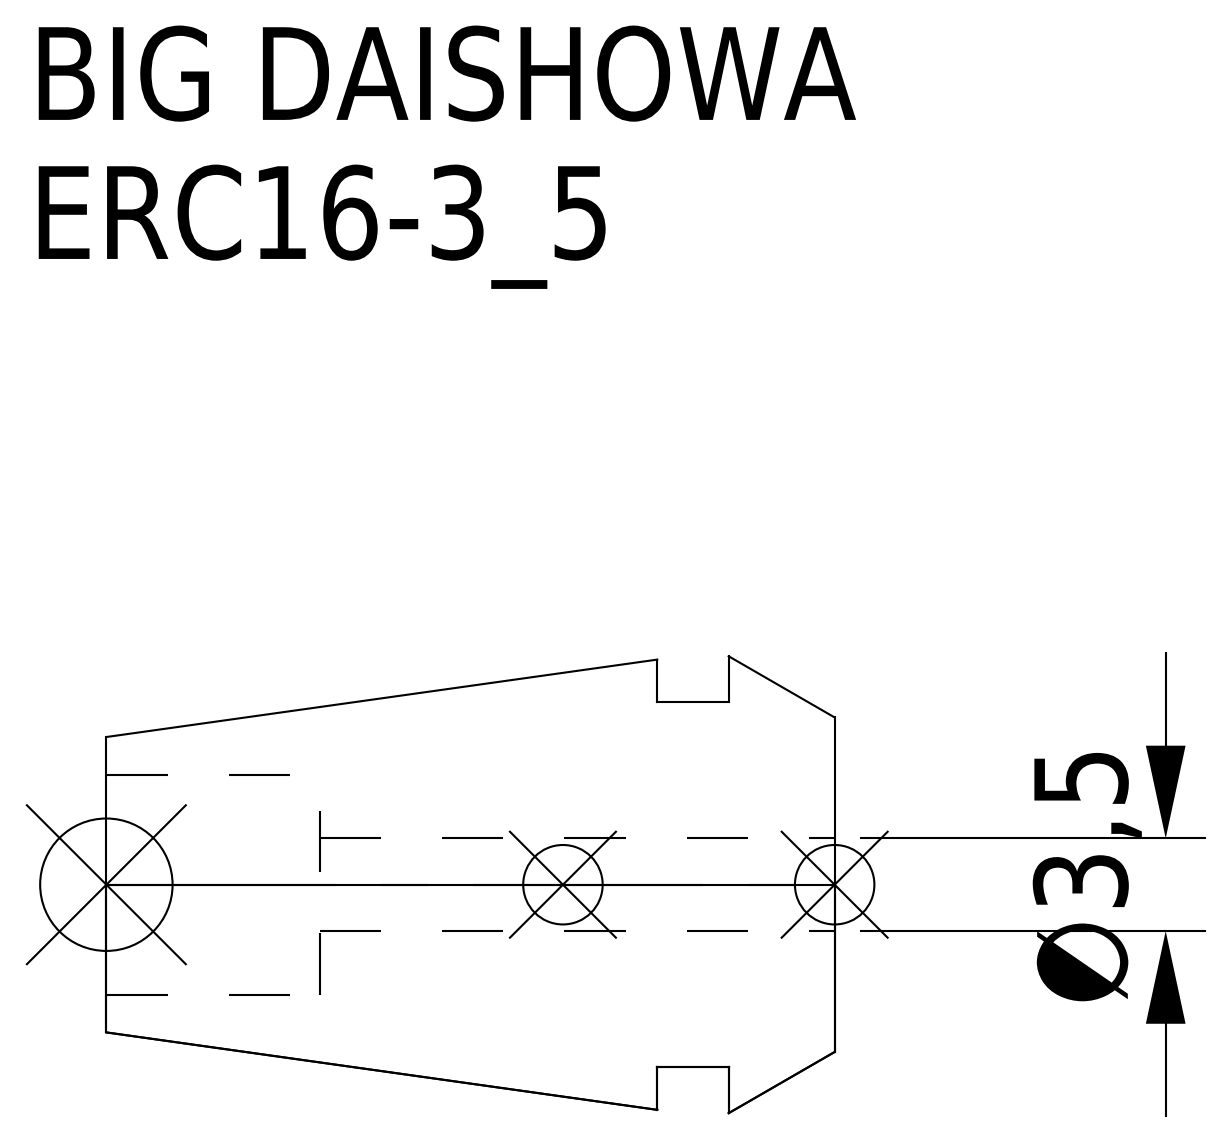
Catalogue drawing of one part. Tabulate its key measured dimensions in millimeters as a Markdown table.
| quantity | value |
| --- | --- |
| part name | ERC16-3_5 |
| STEP written by | CREO PARAMETRIC BY PTC INC, 2016380 (AUTOMOTIVE_DESIGN) |
| units | millimeters |
| bodies | 1 solid, 15 faces (5 planar, 6 cylindrical, 4 other) |
| overall size | 27.5 × 17.25 × 17.25 |
| volume | 3 772 mm³ |
| surface area | 2 052 mm² |
| round holes (diameter × count) | 3.5 × 1, 8.3 × 1 |
| round bosses / shafts (diameter × count) | 13.8 × 1 |
| main face-to-face distances | 4, 6.7, 2.7, 19.44, 15.44, 12.74, 27.5, 23.5, 20.8, 8.06 |
